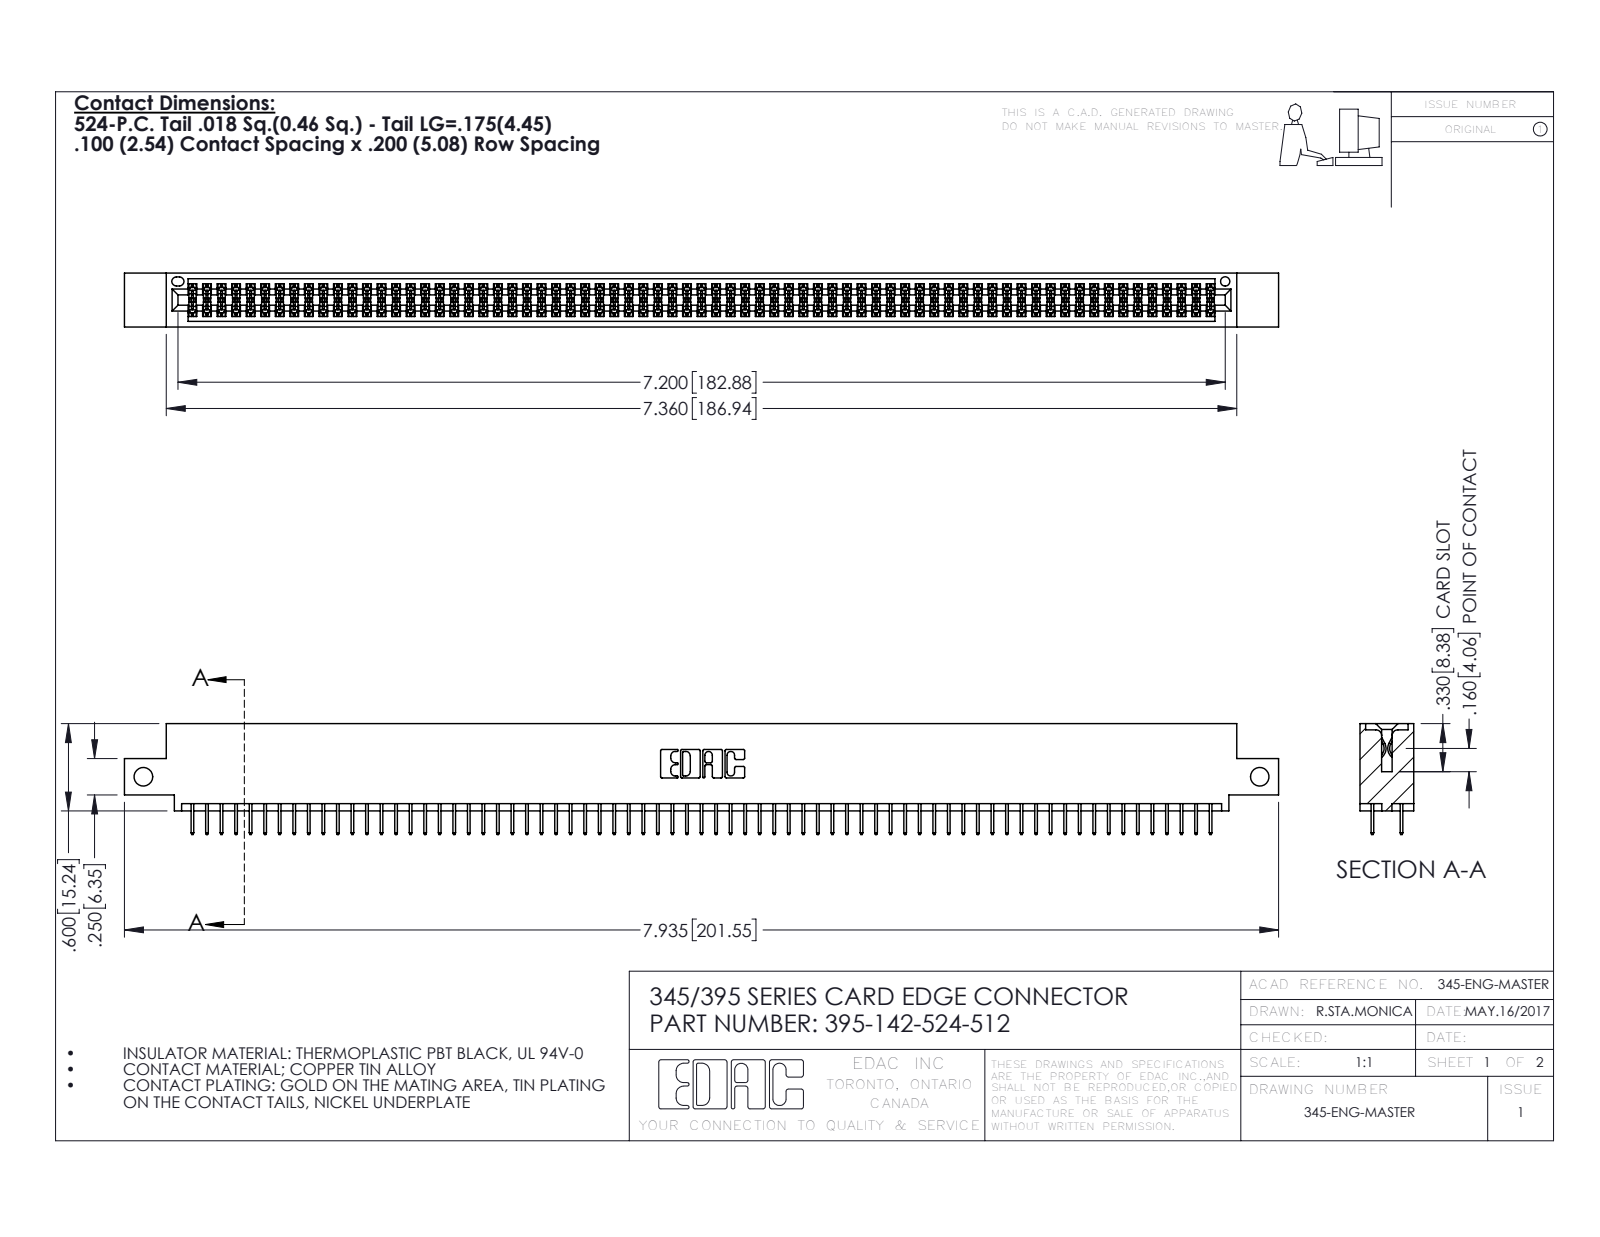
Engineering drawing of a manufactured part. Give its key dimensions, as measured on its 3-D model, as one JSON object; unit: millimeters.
{"part_name": "345-292-001_345-293-124; 395-142-524-512; 345 Part_0.110 Offset - Side Mount", "step_written_by": "SolidWorks 2016 (CONFIG_CONTROL_DESIGN)", "units": "millimeters", "bodies": {"solids": 143, "faces": 7798, "planar": 5622, "cylindrical": 2176, "other": 0}, "overall_size": [201.5, 19.4, 9.4], "volume_mm3": 19470, "surface_area_mm2": 28740, "round_holes": [[3.3, 2], [1.6, 1]], "partial_cylinders_radius": [[0.2, 213], [0.3, 22], [0.2, 6], [0.8, 6], [0.7, 3], [0.4, 2], [0.5, 2], [0.6, 2]], "face_to_face_distances": [1.8, 7.6, 5.1, 9.4, 2.5, 6.9, 0.6, 5.7, 1.8, 4.4], "hole_center_spacings": [194.9]}
